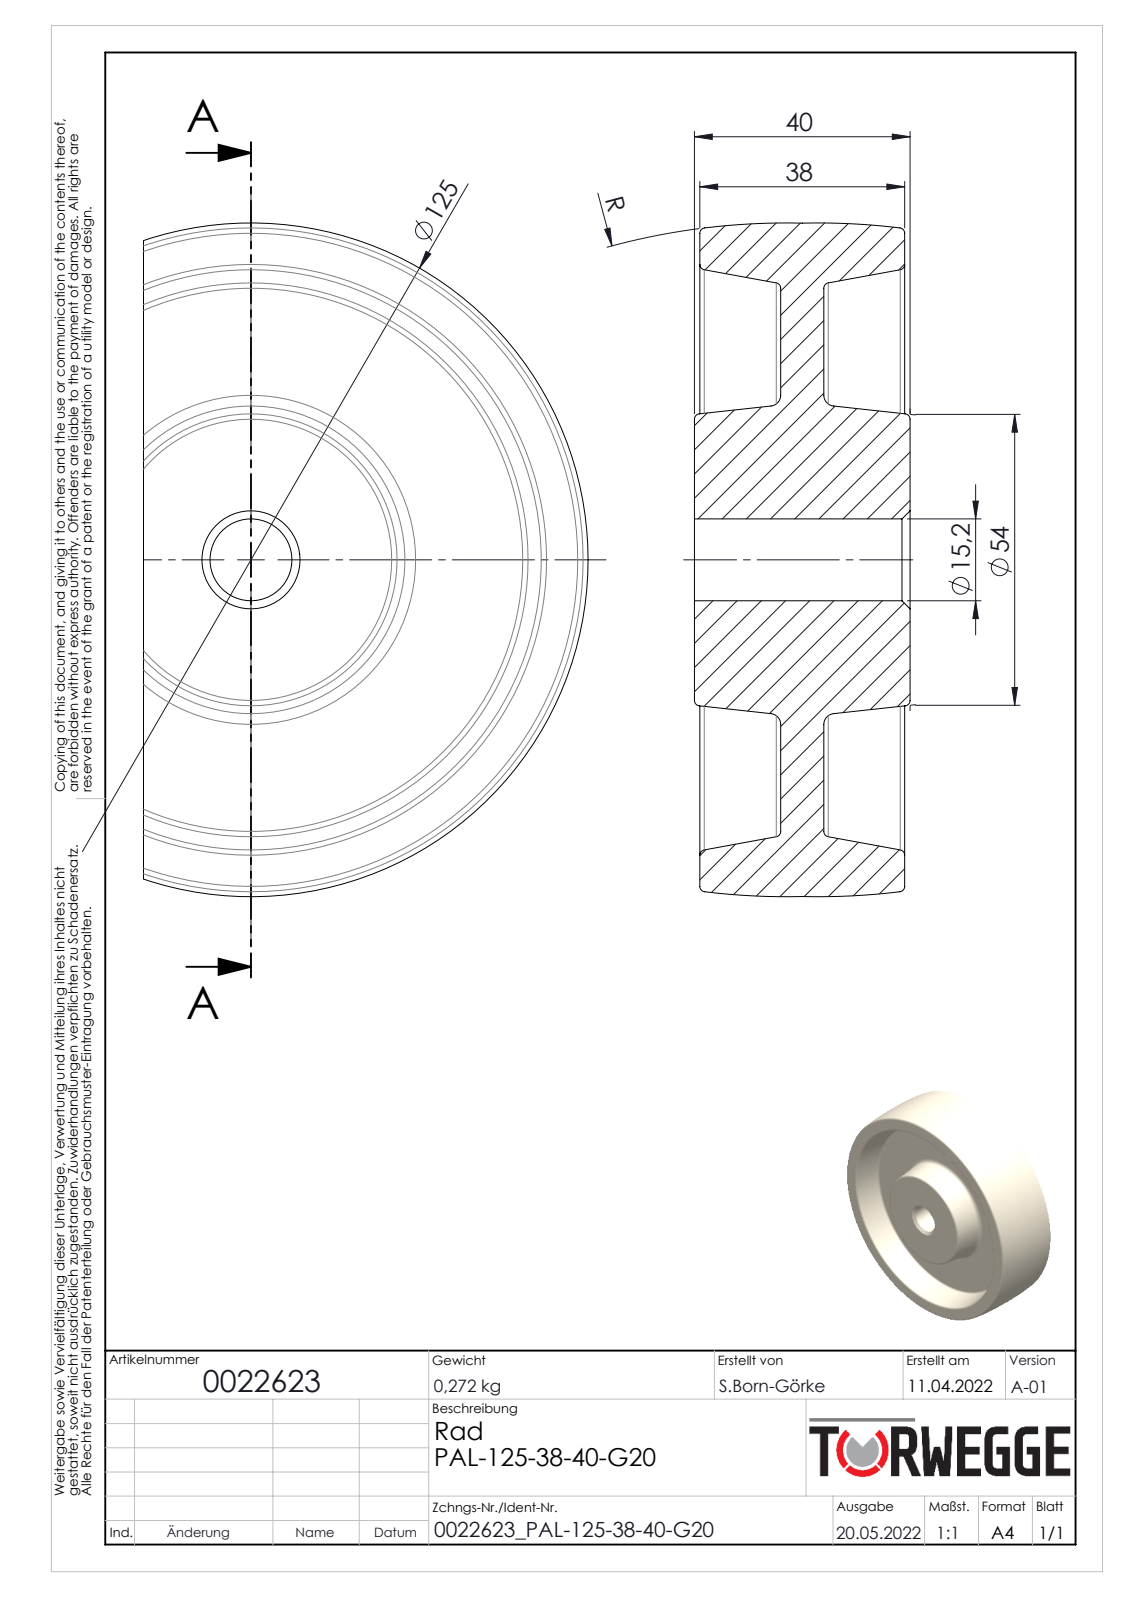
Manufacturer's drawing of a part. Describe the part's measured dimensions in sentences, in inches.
The part is named "0022623". Its 3-D file was written by "SolidWorks 2020 (AUTOMOTIVE_DESIGN)". It is 1 solid with 42 faces: 6 planar, 2 cylindrical and 34 other. Overall it measures 4.924 by 4.924 by 1.575 inches. Its volume is 16.62 cubic inches and its surface area 81.37 square inches. Round holes: 1 of diameter 0.598. The main face-to-face distances are 0.315, 0.591, 0.906, 0.039, 0.63, 0.945, 1.535, 1.496, 1.575.
